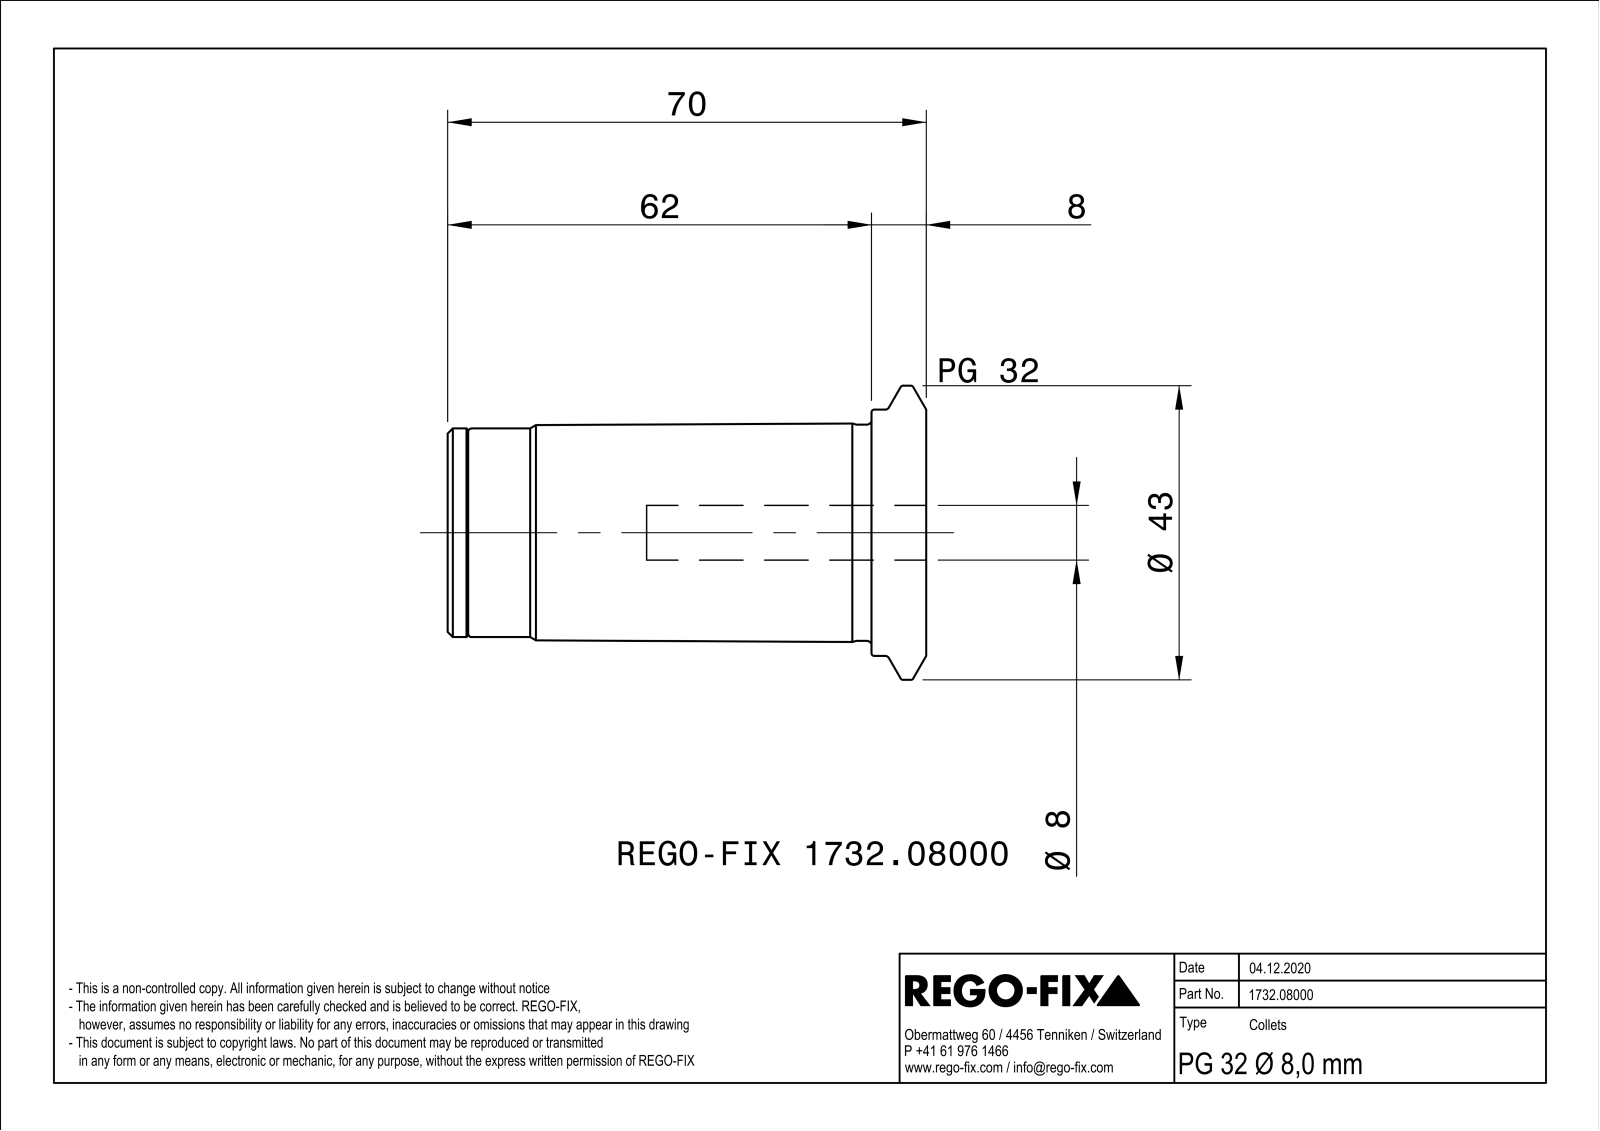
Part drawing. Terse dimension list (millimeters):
name: NOCUT
written by: SIEMENS PLM Software Solid Edge ST10 (AUTOMOTIVE_DESIGN)
unit: mm
bodies: 1 solid, 127 faces (31 planar, 41 cylindrical, 55 other)
size: 70 × 43 × 42.99
volume: 47 718 mm³; area: 16 611 mm²
holes: 3× ⌀4, 1× ⌀8, 1× ⌀8.92, 1× ⌀10.5, 1× ⌀15.5, 1× ⌀26.92, 1× ⌀28.5
bosses: 1× ⌀43, 1× ⌀36, 1× ⌀31.6, 1× ⌀30.5, 1× ⌀26.5, 1× ⌀21
rounds: 6× R2, 3× R3.5, 1× R3.98, 1× R4.75, 1× R8.75
face distances: 1, 70, 58, 12, 59, 11, 8, 60, 2, 10
hole spacings: 7.75, 13.42, 13.43
